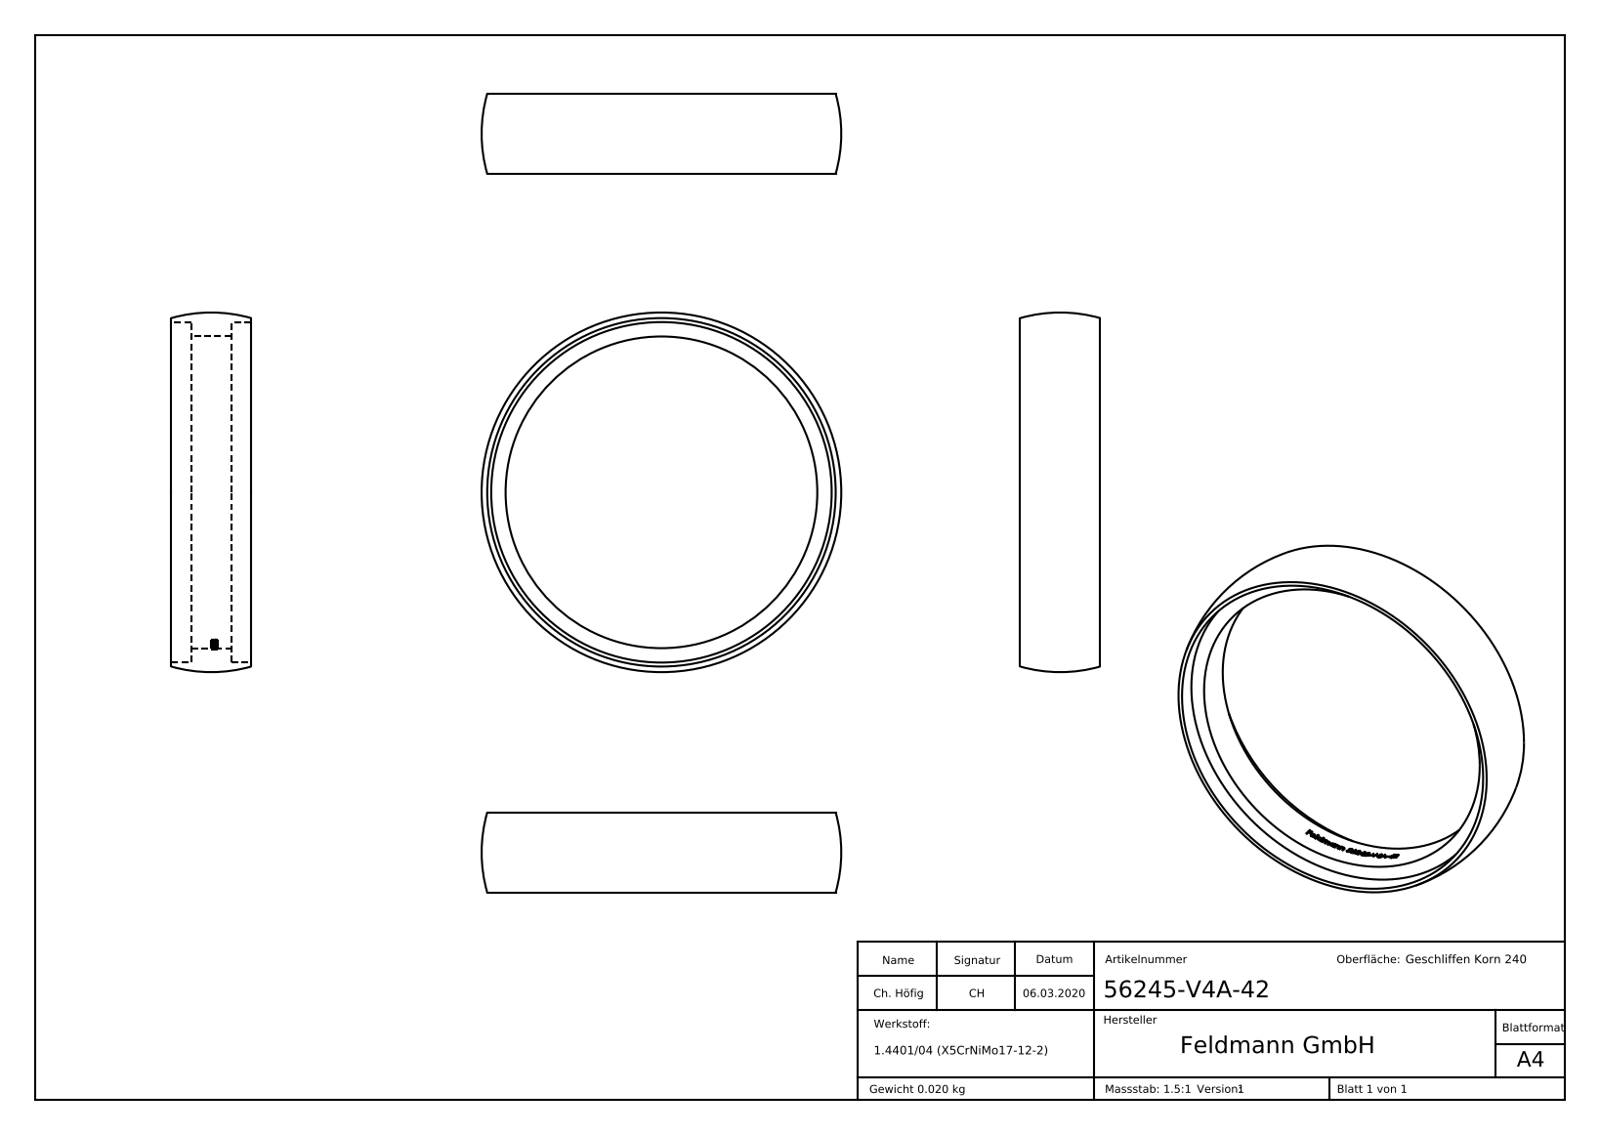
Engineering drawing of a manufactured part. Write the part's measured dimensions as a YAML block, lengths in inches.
part_name: "56245-V4A-42"
step_written_by: "SolidWorks 2015 (CONFIG_CONTROL_DESIGN)"
units: inches
bodies: {solids: 1, faces: 267, planar: 150, cylindrical: 31, other: 86}
overall_size: [1.772, 1.772, 0.394]
volume: 0.151
surface_area: 5.118
round_holes:
  - {diameter: 1.535, count: 1}
  - {diameter: 1.677, count: 1}
partial_cylinders:
  - {radius: 0.772, count: 1}
face_to_face_distances: [0.197, 0.098, 0.295, 0.394, 0.07, 0.021, 0.067, 0.031, 0.033, 0.183]
